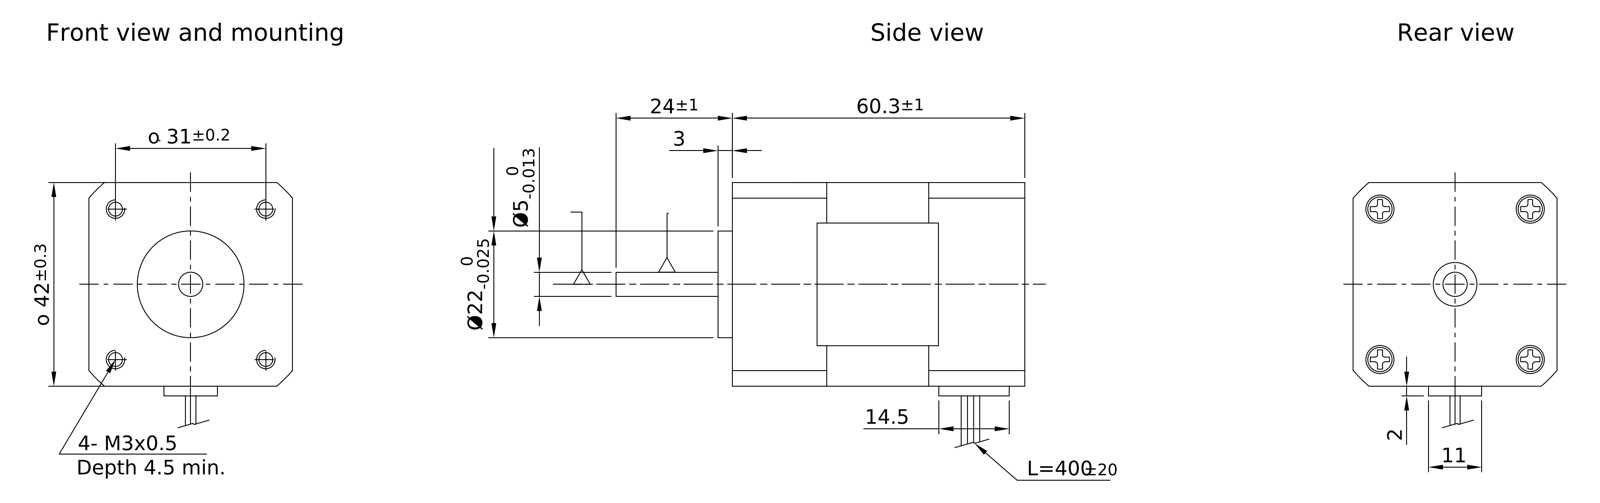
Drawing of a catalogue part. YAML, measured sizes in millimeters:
part_name: "DB41M024030-A"
step_written_by: "Autodesk Inventor 2016 (AUTOMOTIVE_DESIGN)"
units: millimeters
bodies: {solids: 16, faces: 262, planar: 133, cylindrical: 57, other: 72}
overall_size: [84.34, 72, 42]
volume: 103988
surface_area: 25550
round_holes:
  - {diameter: 2.46, count: 4}
  - {diameter: 2.7, count: 4}
  - {diameter: 5.8, count: 4}
  - {diameter: 5, count: 1}
  - {diameter: 6, count: 1}
  - {diameter: 9, count: 1}
round_bosses_or_shafts:
  - {diameter: 1.5, count: 8}
  - {diameter: 2.5, count: 4}
  - {diameter: 2.27, count: 4}
  - {diameter: 22, count: 1}
partial_cylinders:
  - {radius: 5.5, count: 1}
  - {radius: 24.5, count: 1}
  - {radius: 27.5, count: 1}
face_to_face_distances: [42, 32.5, 50.3, 17.8, 10, 42.5, 60.3, 3, 45.5, 2]
hole_center_spacings: [21.92, 31, 43.84]
